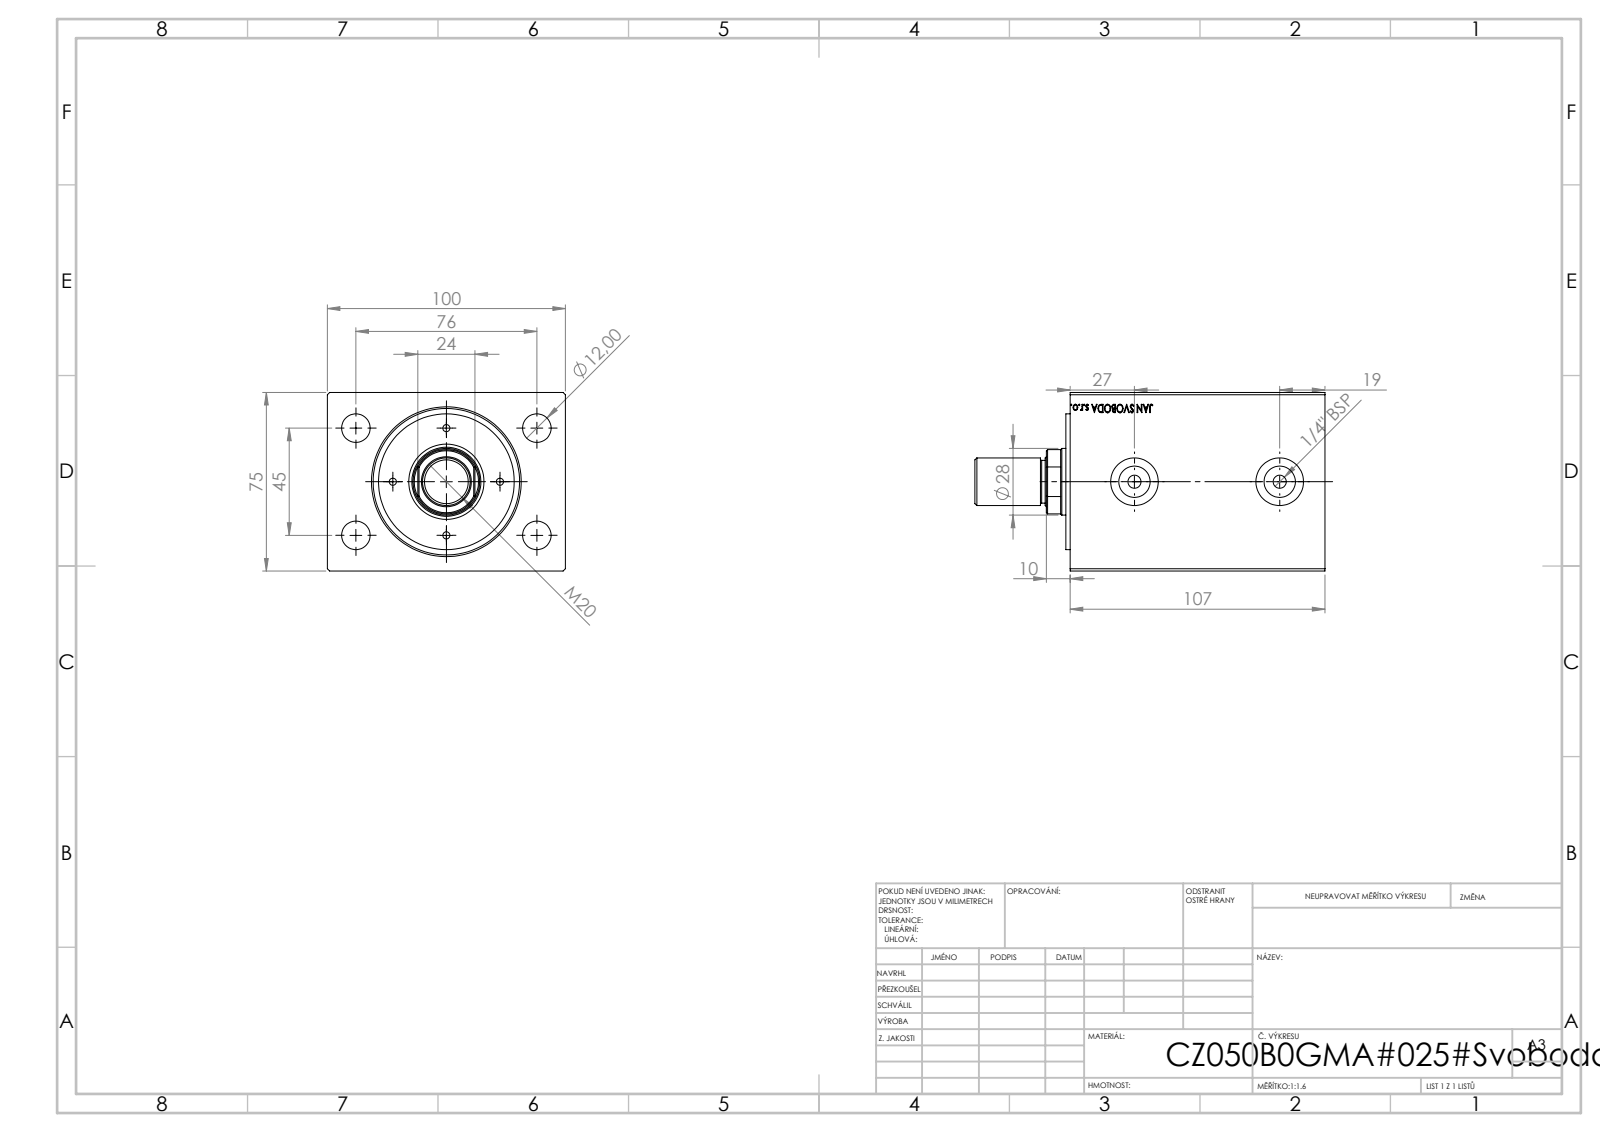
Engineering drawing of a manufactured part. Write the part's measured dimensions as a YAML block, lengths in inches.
part_name: "V500CZ_MALE_METRIC; V500CZ_B_VC; V500CZ"
step_written_by: "SolidWorks 2019 (CONFIG_CONTROL_DESIGN)"
units: inches
bodies: {solids: 4, faces: 888, planar: 404, cylindrical: 62, other: 422}
overall_size: [5.787, 3.937, 2.953]
volume: 45.57
surface_area: 160.6
round_holes:
  - {diameter: 0.118, count: 4}
  - {diameter: 0.472, count: 4}
  - {diameter: 0.217, count: 2}
  - {diameter: 0.518, count: 2}
  - {diameter: 0.787, count: 2}
  - {diameter: 0.728, count: 1}
  - {diameter: 1.102, count: 1}
  - {diameter: 1.142, count: 1}
  - {diameter: 1.417, count: 1}
  - {diameter: 1.969, count: 1}
  - {diameter: 2.421, count: 1}
round_bosses_or_shafts:
  - {diameter: 2.244, count: 1}
  - {diameter: 0.787, count: 1}
  - {diameter: 0.709, count: 1}
partial_cylinders:
  - {radius: 0.531, count: 1}
face_to_face_distances: [2.953, 3.937, 4.213, 3.512, 0.701, 0.394, 0.323, 0.071, 3.189, 3.89]
hole_center_spacings: [0.886, 1.076, 1.253, 1.496, 1.739, 1.772, 2.319, 2.541]
